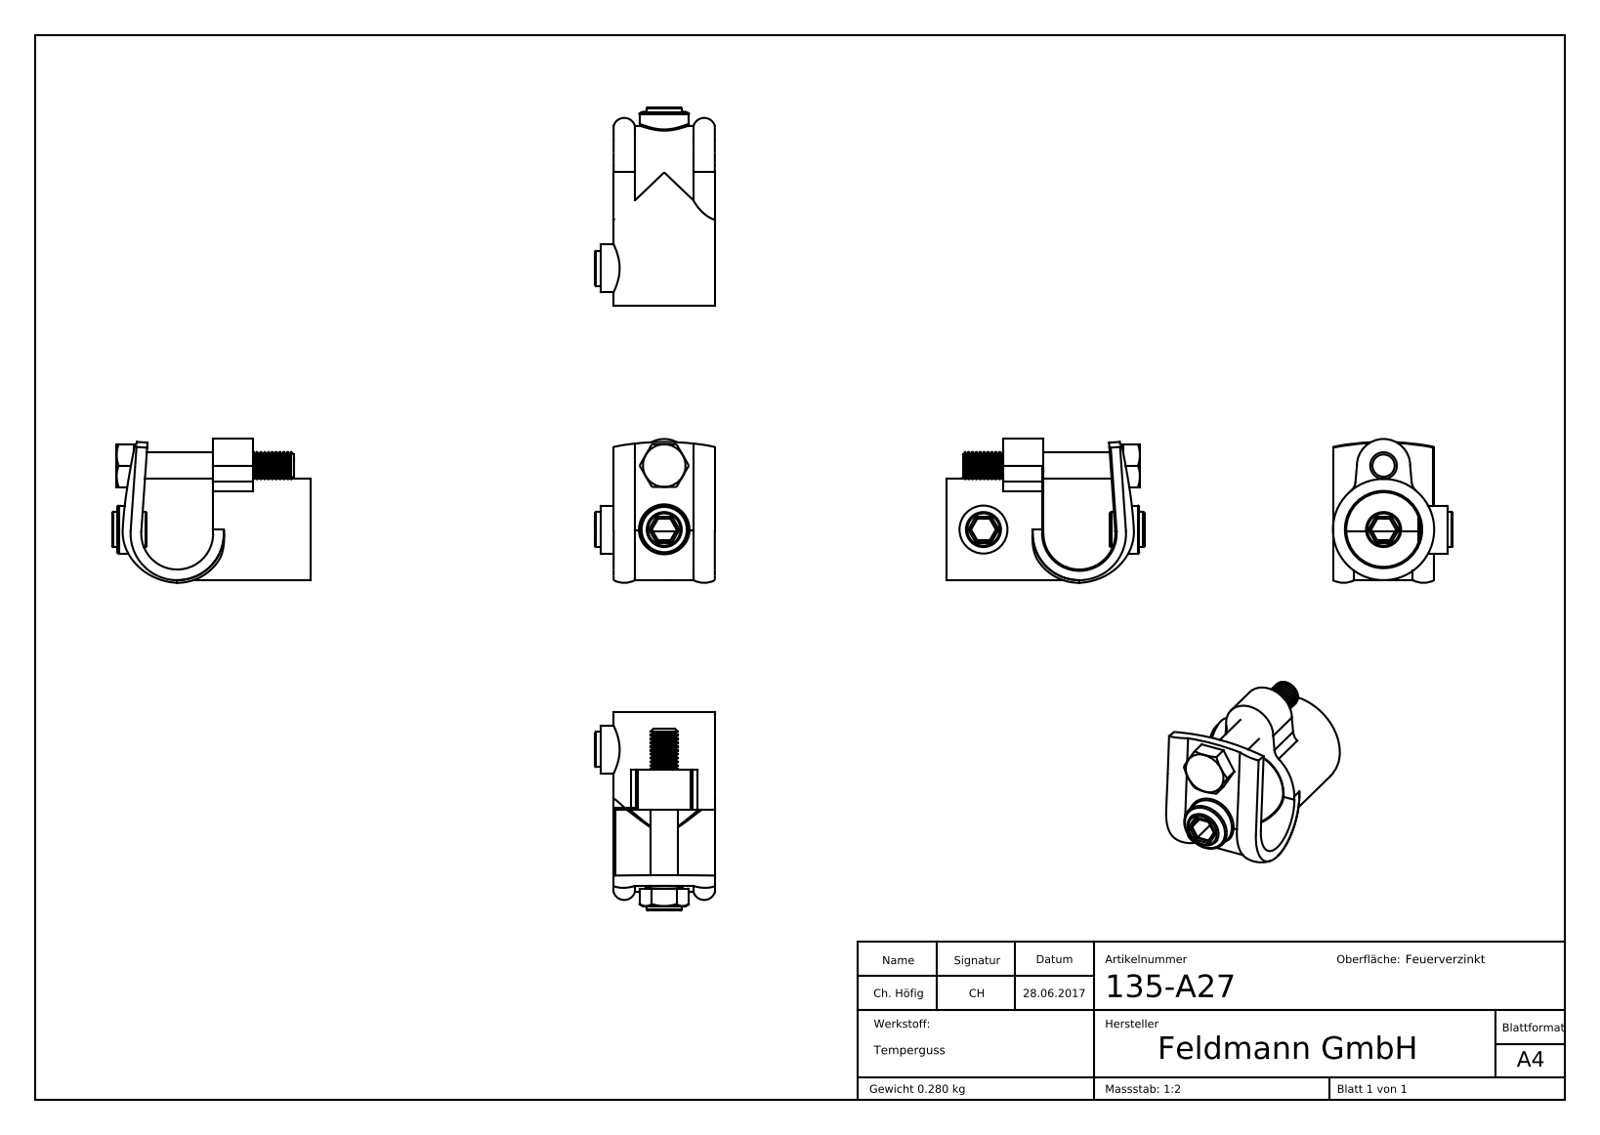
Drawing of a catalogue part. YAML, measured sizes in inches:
part_name: "135-A27; 135-A27 Teil2; hex bolt gradeb_din_ISO 4015 - M10 x 60 x 26-S; 135-C42 Teil1_135-A27 Teil1 (+2 more)"
step_written_by: "SolidWorks 2018 (CONFIG_CONTROL_DESIGN)"
units: inches
bodies: {solids: 4, faces: 191, planar: 65, cylindrical: 64, other: 62}
overall_size: [2.931, 2.126, 1.772]
volume: 2.642
surface_area: 35.18
round_holes:
  - {diameter: 0.465, count: 2}
  - {diameter: 0.335, count: 1}
  - {diameter: 0.512, count: 1}
  - {diameter: 1.102, count: 1}
round_bosses_or_shafts:
  - {diameter: 0.709, count: 2}
  - {diameter: 0.518, count: 2}
  - {diameter: 1.496, count: 1}
  - {diameter: 0.394, count: 1}
partial_cylinders:
  - {radius: 0.039, count: 24}
  - {radius: 0.02, count: 3}
  - {radius: 0.197, count: 2}
  - {radius: 0.689, count: 2}
  - {radius: 0.394, count: 1}
  - {radius: 0.531, count: 1}
  - {radius: 3.778, count: 1}
face_to_face_distances: [1.437, 0.157, 1.496, 0.591, 0.846, 0.319, 2.863, 2.017, 1.426, 0.63]
hole_center_spacings: [0.945]
